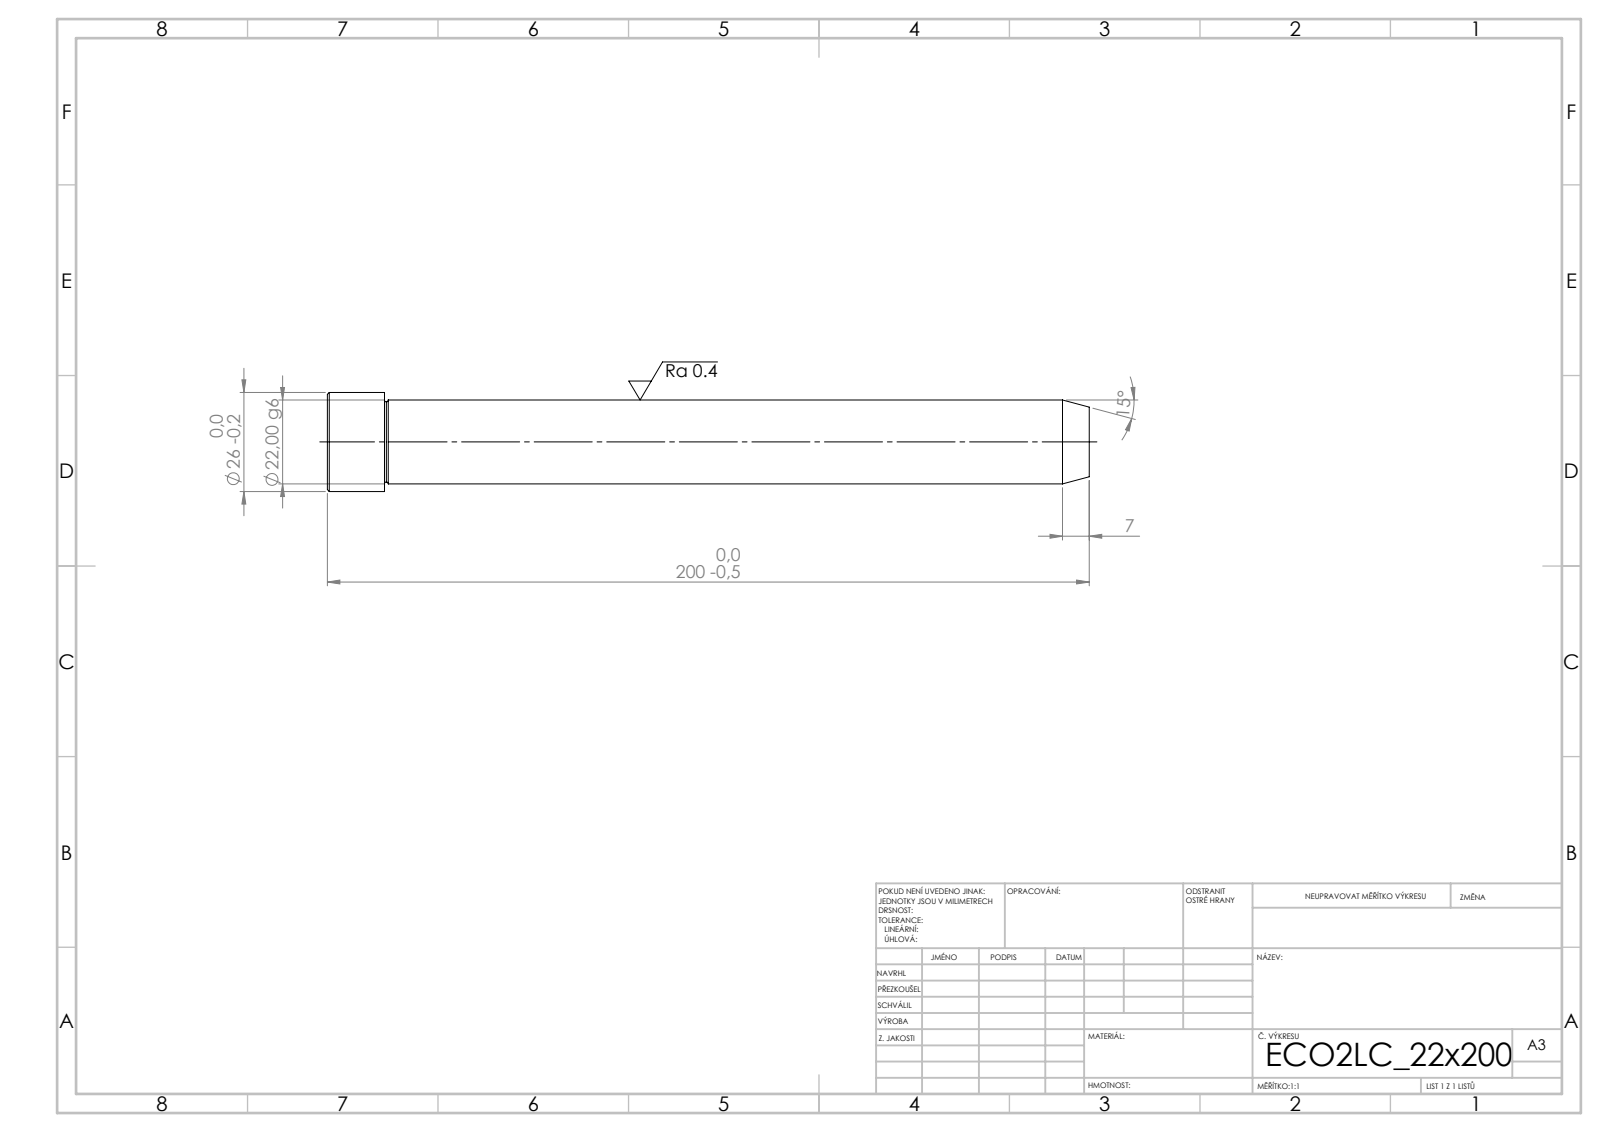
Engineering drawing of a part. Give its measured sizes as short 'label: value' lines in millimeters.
written by: SolidWorks 2019 (CONFIG_CONTROL_DESIGN)
unit: mm
bodies: 1 solid, 15 faces (3 planar, 4 cylindrical, 8 other)
size: 200 × 26 × 26
volume: 77 824 mm³; area: 14 941 mm²
bosses: 1× ⌀26, 1× ⌀22
face distances: 200, 185, 15
